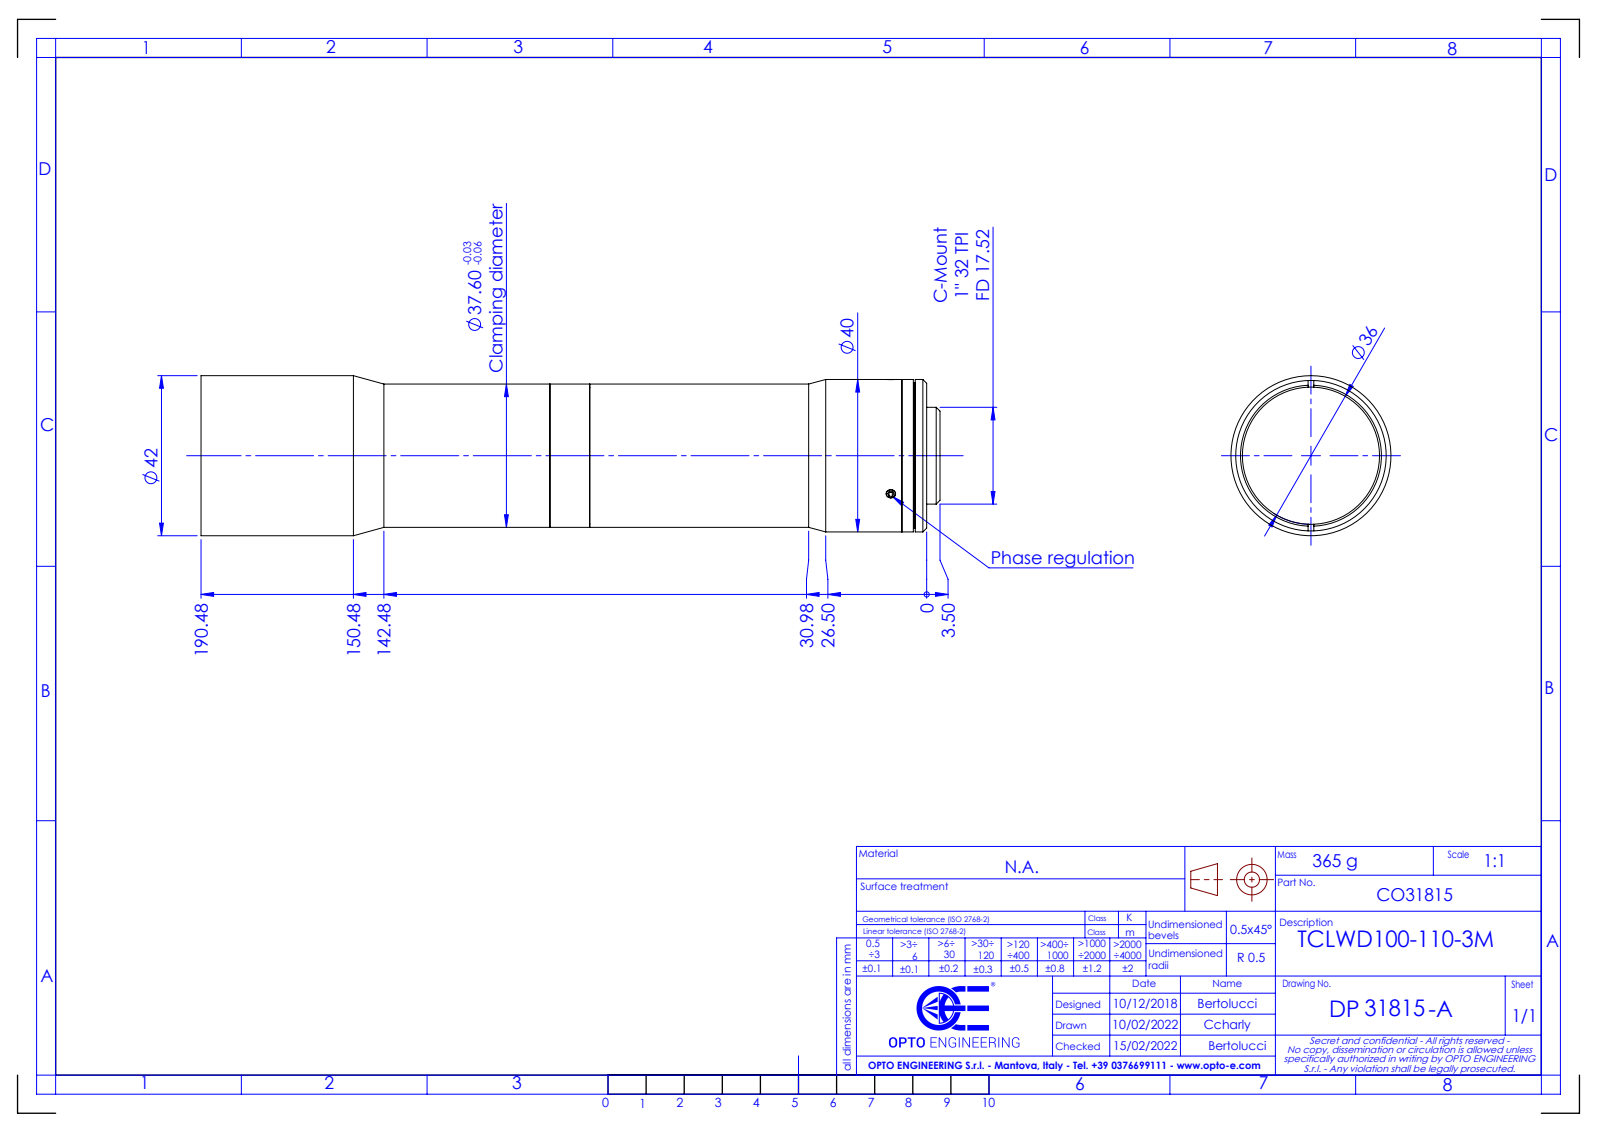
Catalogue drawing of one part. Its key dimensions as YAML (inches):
part_name: "DP31815-A_TCLWD100-110-3M"
step_written_by: "SolidWorks 2021 (CONFIG_CONTROL_DESIGN)"
units: inches
bodies: {solids: 0, faces: 84, planar: 39, cylindrical: 26, other: 19}
overall_size: [7.637, 1.654, 1.654]
round_holes:
  - {diameter: 0.886, count: 1}
  - {diameter: 1.004, count: 1}
  - {diameter: 1.26, count: 1}
  - {diameter: 1.417, count: 1}
  - {diameter: 1.555, count: 1}
round_bosses_or_shafts:
  - {diameter: 1.654, count: 1}
  - {diameter: 1.575, count: 1}
  - {diameter: 1.48, count: 1}
  - {diameter: 1, count: 1}
face_to_face_distances: [0.138, 0.118, 0.02, 3.343, 3.362, 3.48, 0.256, 3.224, 4.011, 7.235]
